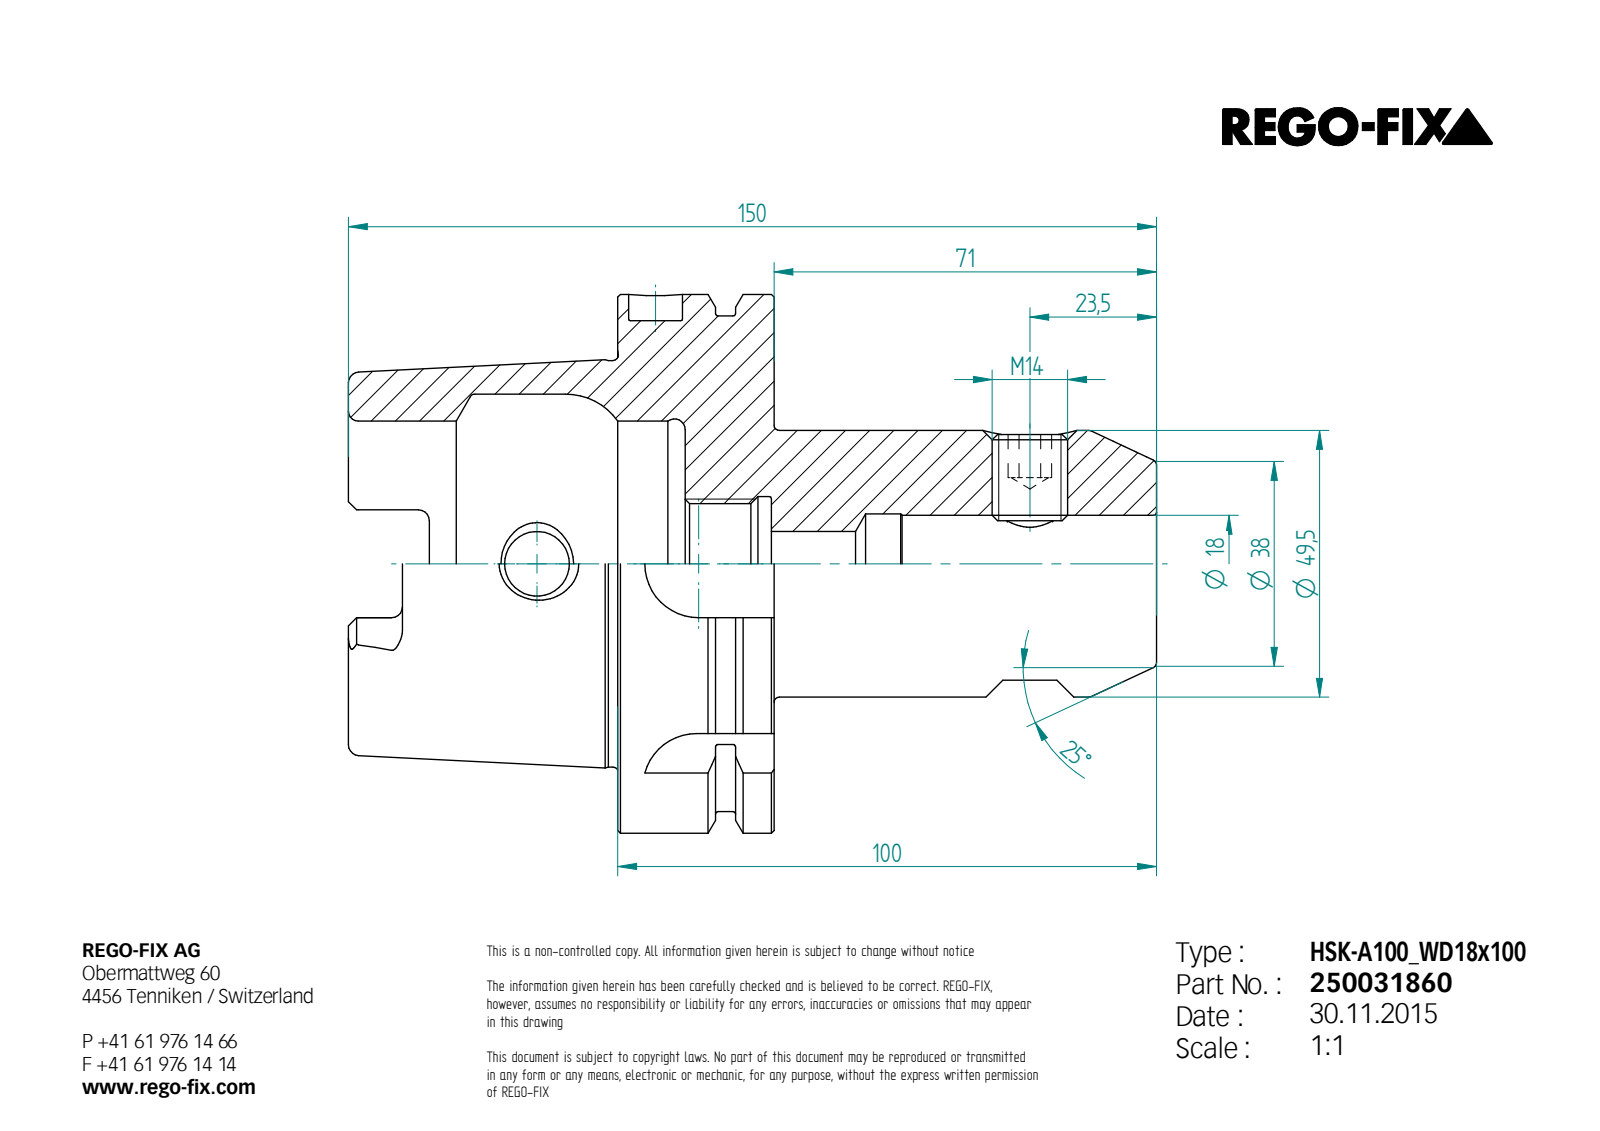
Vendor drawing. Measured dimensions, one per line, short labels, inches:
written by: Unknown (AUTOMOTIVE_DESIGN)
unit: in
bodies: 2 solids, 144 faces (52 planar, 36 cylindrical, 56 other)
size: 5.906 × 3.937 × 3.937
volume: 22.54 in³; area: 100.2 in²
holes: 2× ⌀0.472, 1× ⌀0.335, 1× ⌀0.394, 1× ⌀0.466, 1× ⌀0.709, 1× ⌀0.728, 1× ⌀0.881, 1× ⌀0.984, 1× ⌀2.087, 1× ⌀2.48
bosses: 1× ⌀3.937, 1× ⌀3.622, 1× ⌀2.971, 1× ⌀1.949, 1× ⌀0.551
rounds: 6× R0.079, 4× R0.192, 2× R0.394, 1× R0.433
face distances: 1.142, 0.492, 0.65, 3.937, 3.445, 2.795, 1.969, 2.461, 3.11, 5.906
hole spacings: 2.736
